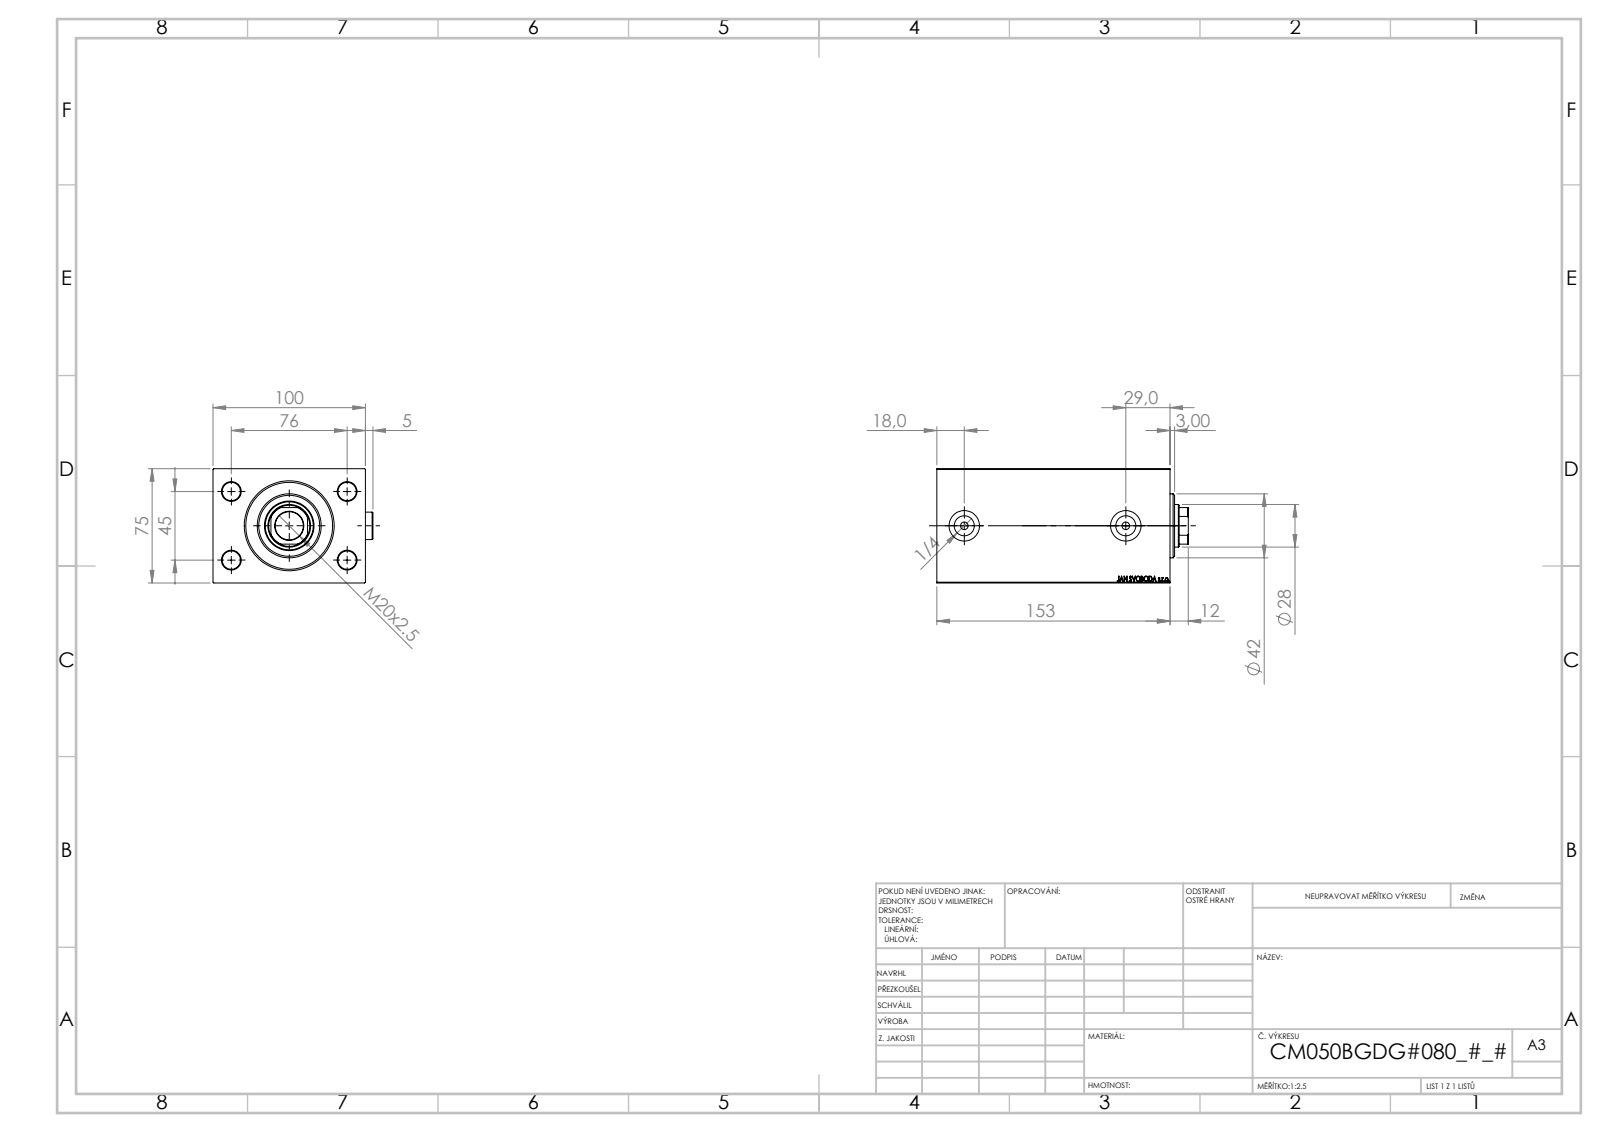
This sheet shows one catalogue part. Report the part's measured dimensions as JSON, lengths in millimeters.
{"part_name": "Zatka_OIL_PORT; V450CM_VC_B; V450CM_B_VCP; V450CM_B_Body", "step_written_by": "SolidWorks 2019 (CONFIG_CONTROL_DESIGN)", "units": "millimeters", "bodies": {"solids": 5, "faces": 938, "planar": 436, "cylindrical": 72, "other": 430}, "overall_size": [165, 104.9, 75], "volume_mm3": 1016000, "surface_area_mm2": 130386, "round_holes": [[12, 4], [5, 2], [13.16, 2], [20, 2], [18.5, 1], [28, 1], [31.5, 1], [32.5, 1], [50, 1], [52, 1], [57, 1]], "round_bosses_or_shafts": [[18, 2], [42, 1]], "partial_cylinders_radius": [[13.5, 1]], "face_to_face_distances": [75, 100, 153, 14, 139, 12, 127, 141, 47, 61], "hole_center_spacings": [44.16, 45, 76, 88.32, 106]}
